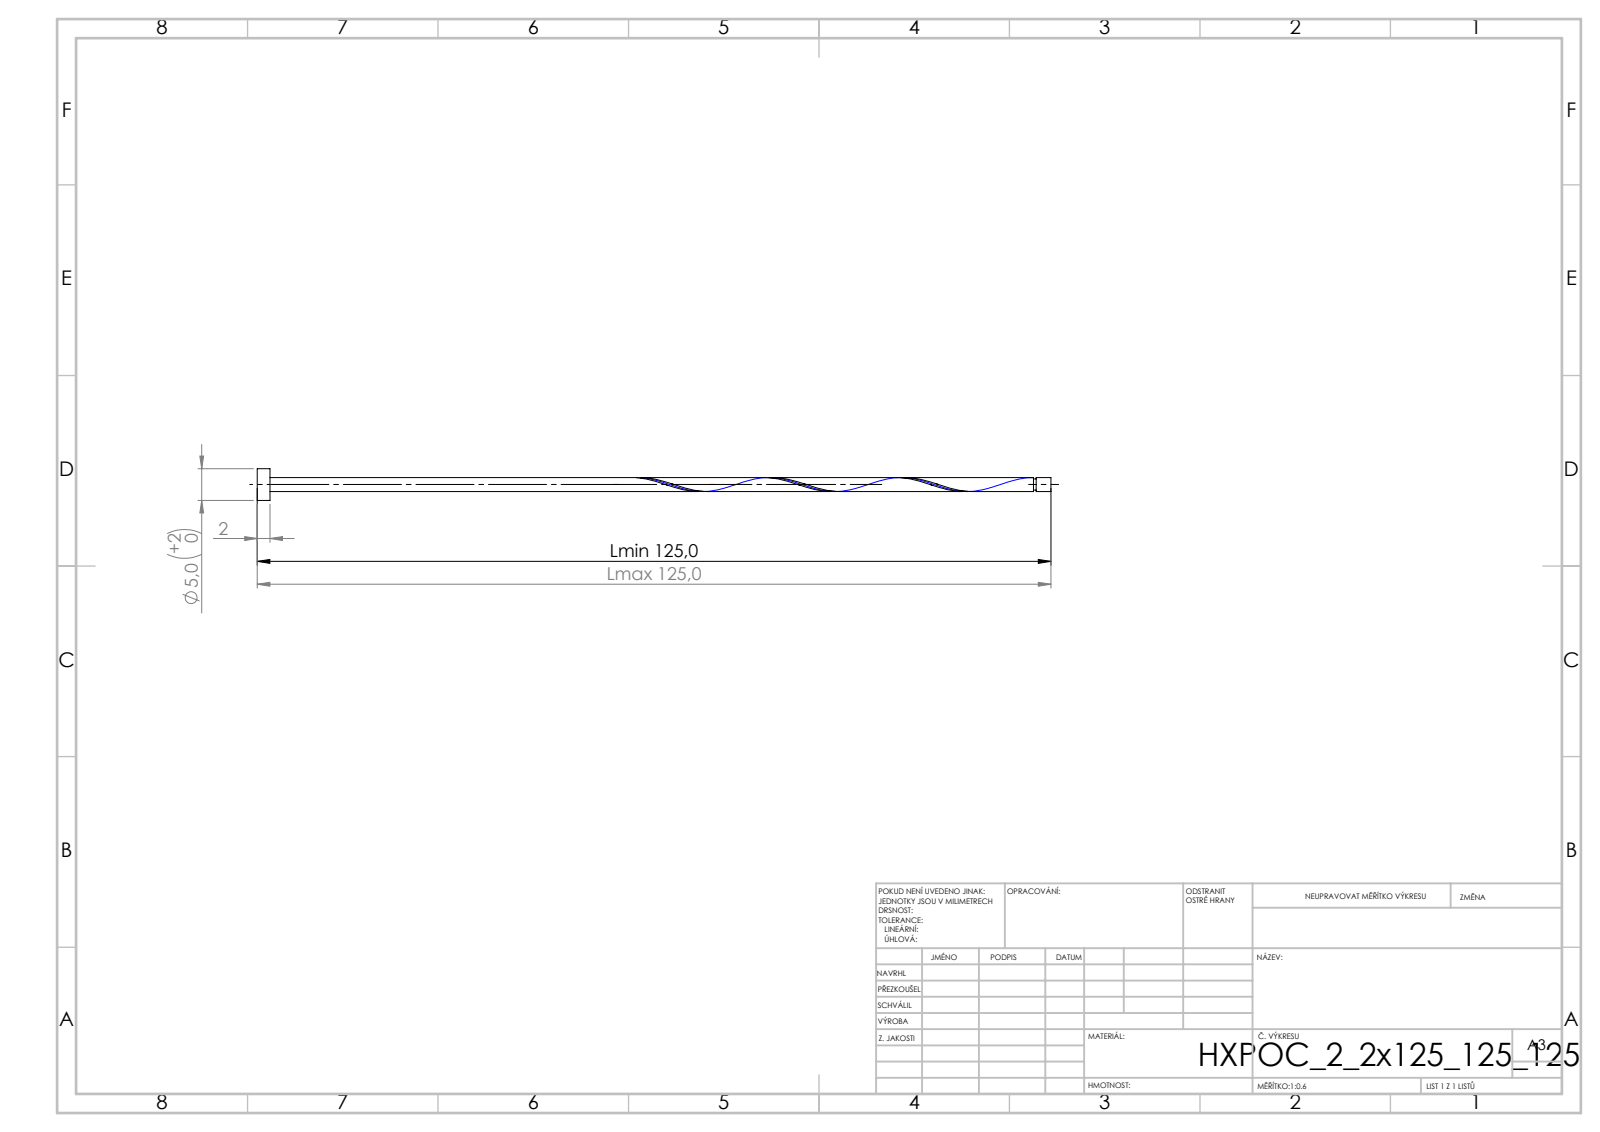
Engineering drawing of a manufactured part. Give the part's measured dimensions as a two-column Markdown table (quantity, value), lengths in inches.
| quantity | value |
| --- | --- |
| STEP written by | SolidWorks 2019 (CONFIG_CONTROL_DESIGN) |
| units | inches |
| bodies | 1 solid, 16 faces (6 planar, 9 cylindrical, 1 other) |
| overall size | 4.921 × 0.197 × 0.197 |
| volume | 0.037 in³ |
| surface area | 1.899 in² |
| round bosses / shafts (diameter × count) | 0.197 × 1, 0.087 × 1, 0.069 × 1 |
| main face-to-face distances | 0.079, 4.921, 4.843, 4.83, 4.751, 0.091, 4.813, 4.734, 0.017, 0.109 |
